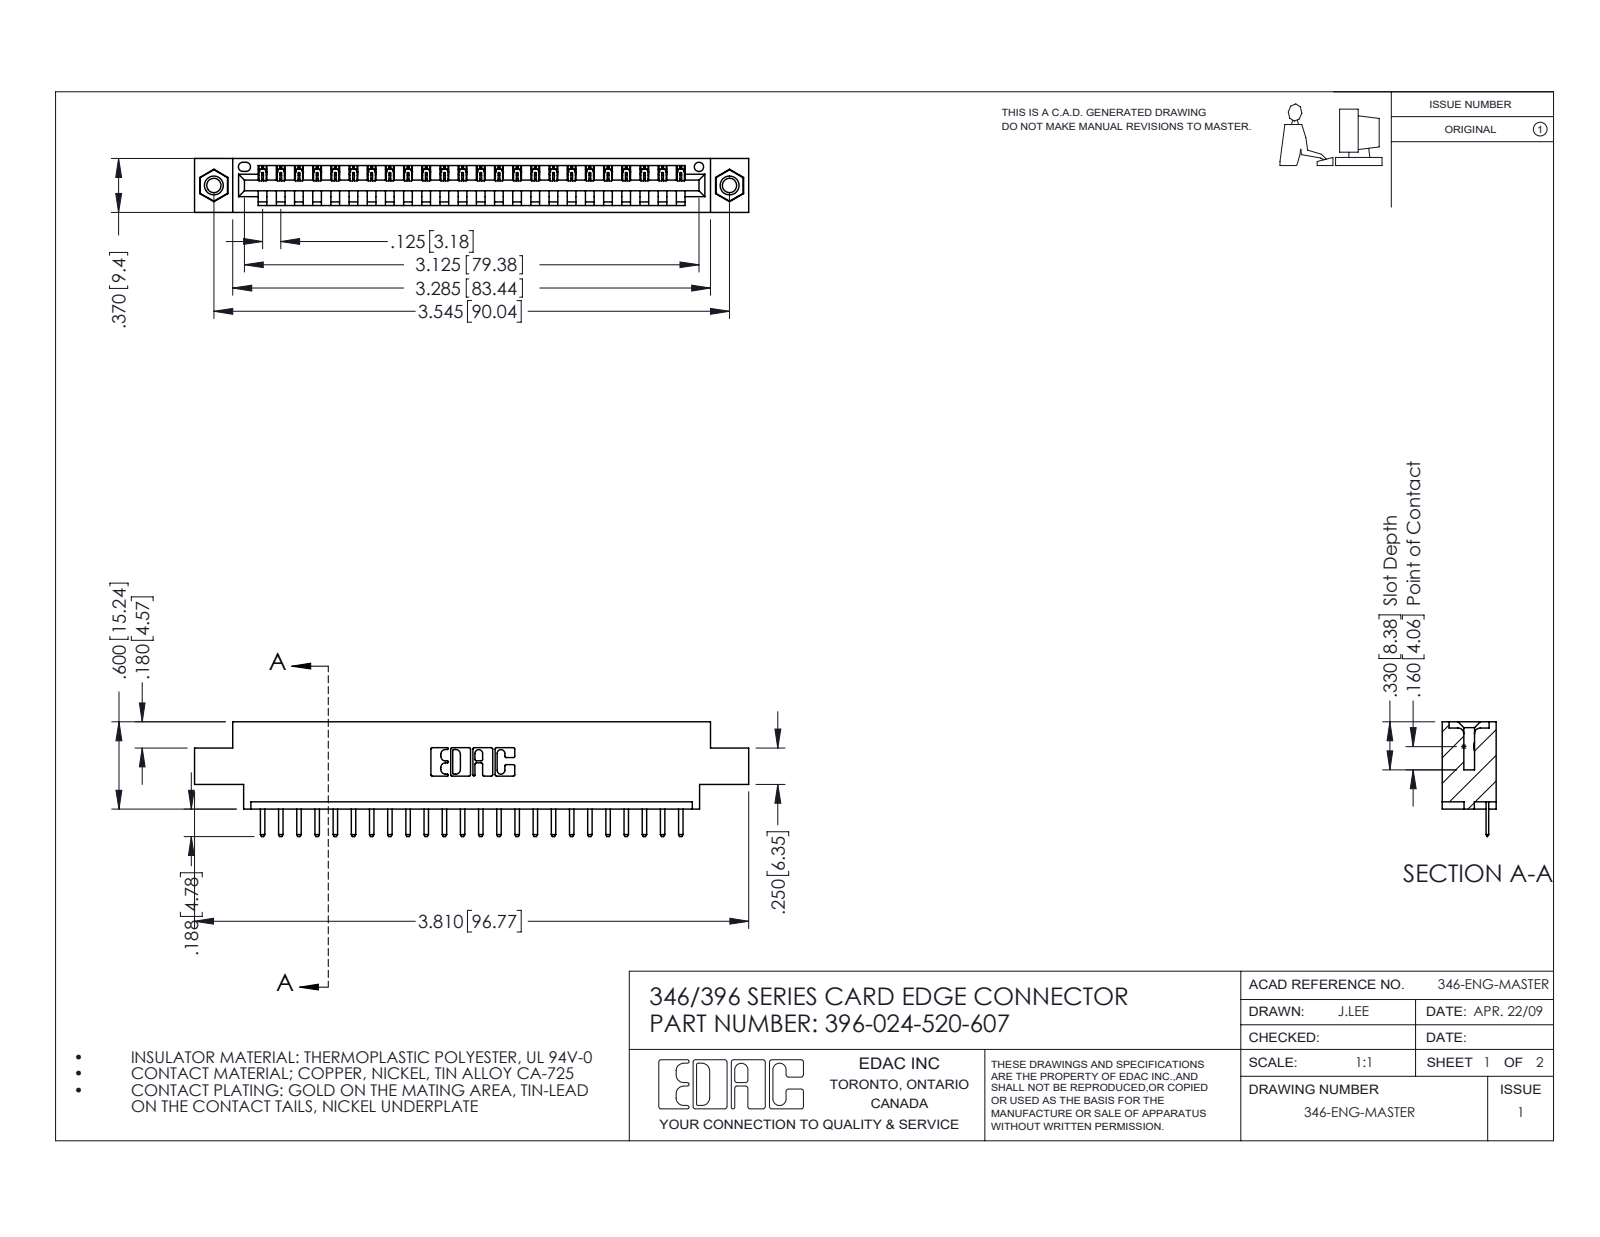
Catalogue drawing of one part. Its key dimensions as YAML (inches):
part_name: "345-292-001_345-293-120; 345-250-001_345-250-005-103; 346 Part_0.170 Offset - 0.156 Dia-TI; 396-024-520-607"
step_written_by: "SolidWorks 2016 (CONFIG_CONTROL_DESIGN)"
units: inches
bodies: {solids: 27, faces: 1674, planar: 1120, cylindrical: 538, other: 16}
overall_size: [3.81, 0.788, 0.37]
volume: 0.543
surface_area: 16.89
round_holes:
  - {diameter: 0.098, count: 2}
  - {diameter: 0.125, count: 2}
  - {diameter: 0.156, count: 2}
  - {diameter: 0.064, count: 1}
round_bosses_or_shafts:
  - {diameter: 0.155, count: 2}
partial_cylinders:
  - {radius: 0.01, count: 50}
  - {radius: 0.006, count: 48}
  - {radius: 0.01, count: 22}
  - {radius: 0.007, count: 6}
  - {radius: 0.031, count: 6}
  - {radius: 0.026, count: 3}
  - {radius: 0.031, count: 2}
  - {radius: 0.04, count: 2}
face_to_face_distances: [0.048, 0.322, 0.37, 0.25, 0.222, 0.148, 0.1, 0.174, 0.072, 0.298]
hole_center_spacings: [0.246, 3.337, 3.545]
